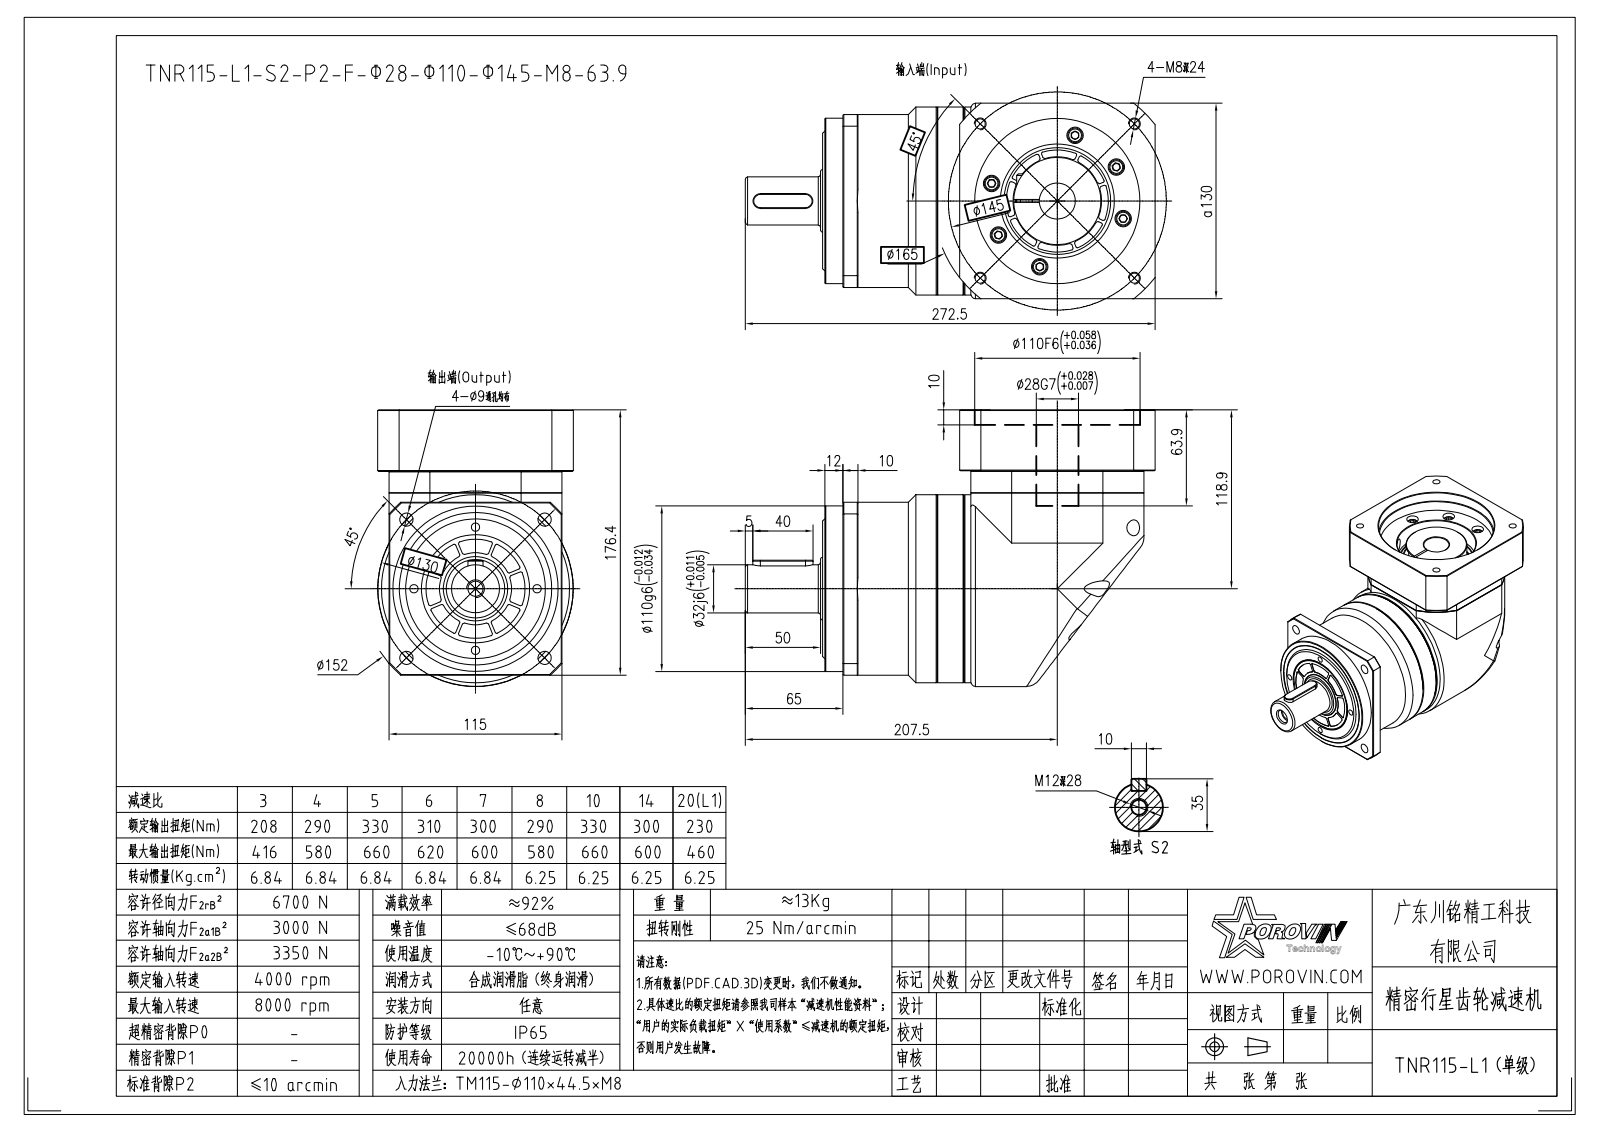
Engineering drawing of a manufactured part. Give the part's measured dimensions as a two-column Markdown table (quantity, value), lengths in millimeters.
| quantity | value |
| --- | --- |
| part name | SPRING_LOCK_WASHERS--NORMAL_TYP; HEXAGON_SOCKET_HEAD_CAP_S-14853; HEXAGON_SOCKET_COUNTERSUNK_HEAD; TNR115280001 (+8 more) |
| STEP written by | CREO PARAMETRIC BY PTC INC, 2020053 (CONFIG_CONTROL_DESIGN) |
| units | millimeters |
| bodies | 50 solids, 1381 faces (575 planar, 556 cylindrical, 250 other) |
| overall size | 272.5 × 183.9 × 130 |
| volume | 2 901 000 mm³ |
| surface area | 351 971 mm² |
| round holes (diameter × count) | 6.68 × 19, 6.5 × 13, 11 × 12, 5 × 8, 10.5 × 7, 6.6 × 6, 6.8 × 5, 5.5 × 4, 9 × 4, 72 × 2, 8.5 × 1, 10.2 × 1 |
| round bosses / shafts (diameter × count) | 10 × 19, 9.88 × 19, 6 × 19, 130 × 1, 125 × 1, 124 × 1, 115 × 1, 110 × 1 |
| partial cylindrical surfaces (radius × count) | 1 × 64, 5 × 3, 6.75 × 1, 10 × 1, 65 × 1, 76 × 1, 82.5 × 1 |
| main face-to-face distances | 18, 17.8, 14.9, 7.5, 122.5, 3, 20, 55.4, 130, 40.5 |
| hole center spacings | 45.25, 57.25, 46.18, 51.41, 98.8, 111.28, 91.96, 46.42 |
